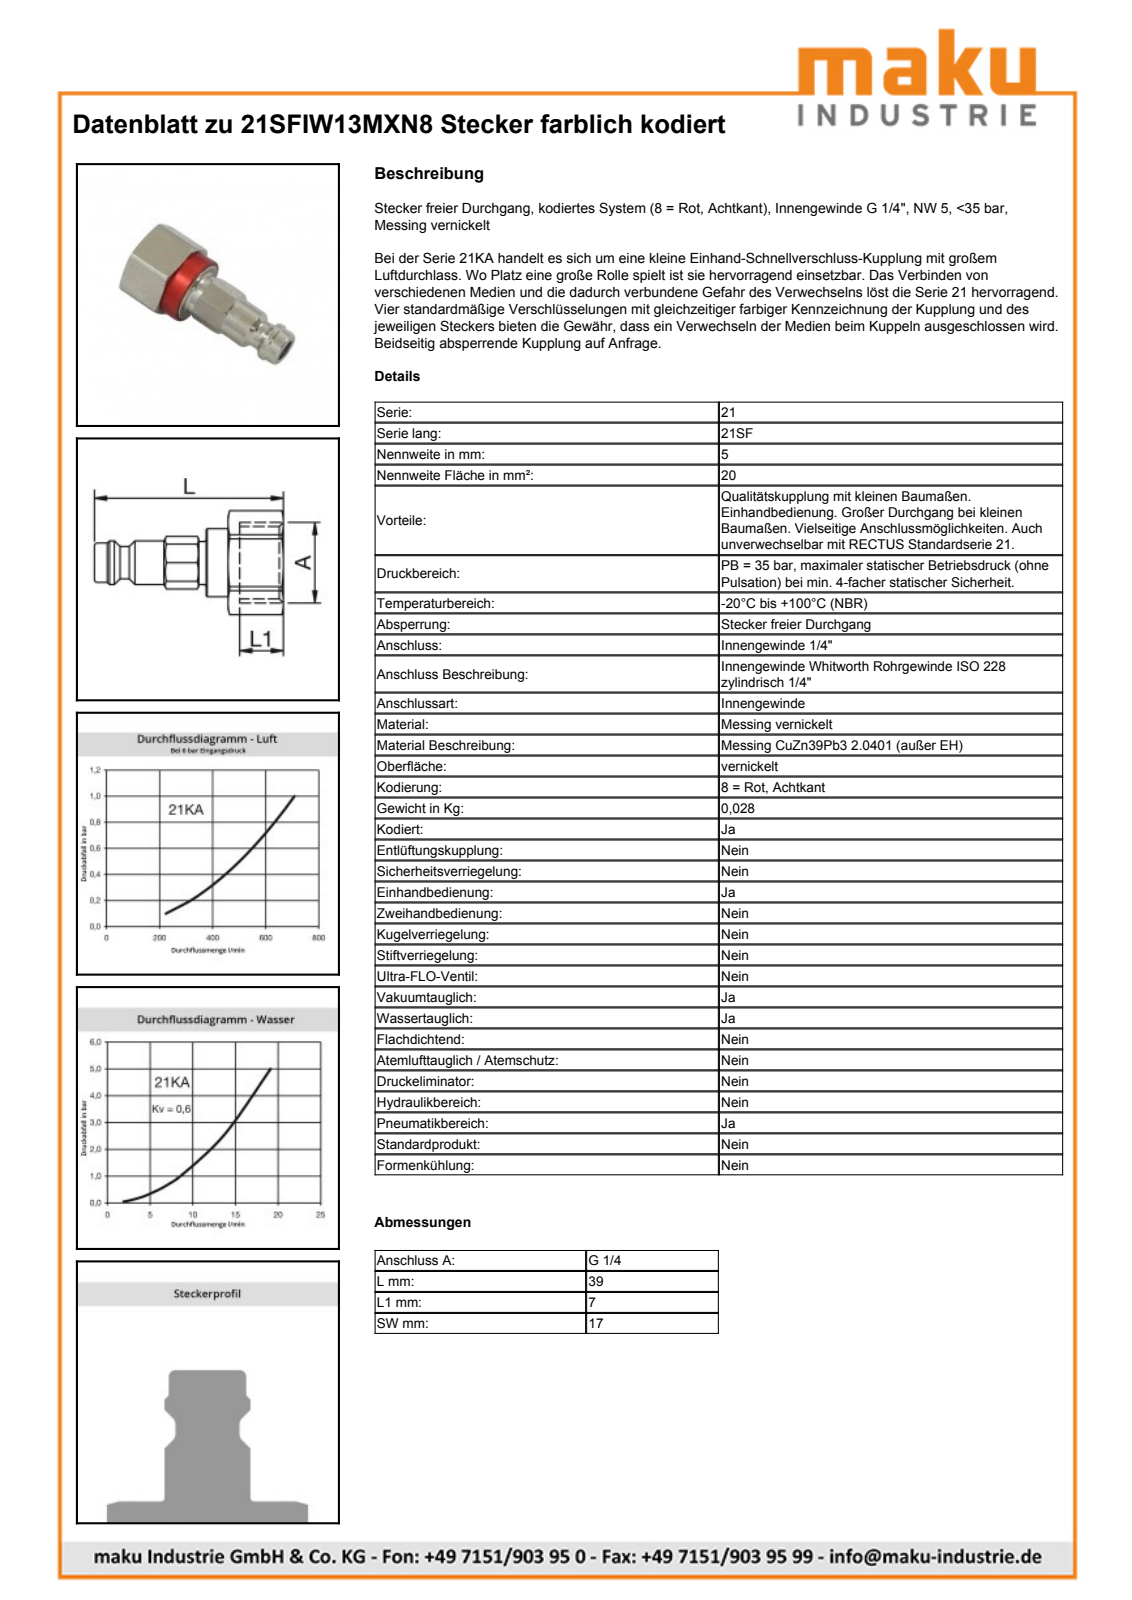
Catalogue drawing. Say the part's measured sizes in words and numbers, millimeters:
The part is named "D110302; D110301; D104771". Its 3-D file was written by "Autodesk Inventor 2013 (AUTOMOTIVE_DESIGN)". It is 2 solids with 72 faces: 21 planar, 25 cylindrical and 26 other. Overall it measures 39 by 19.15 by 17 millimeters. Its volume is 3 594 cubic millimeters and its surface area 3 182 square millimeters. Round holes: 1 of diameter 4.95, 1 of diameter 11.45, 1 of diameter 13.85, 1 of diameter 14.05. Round bosses or shafts: 1 of diameter 15.5, 1 of diameter 14, 1 of diameter 9.7, 1 of diameter 9, 1 of diameter 8.1, 1 of diameter 6.65. Partial cylindrical surfaces (rounded edges, fillets, slot ends): 1 of radius 5.35, 1 of radius 9.57. The main face-to-face distances are 17, 10, 11, 2, 9, 4.5, 6.5, 15.5, 3.5, 13.5.
